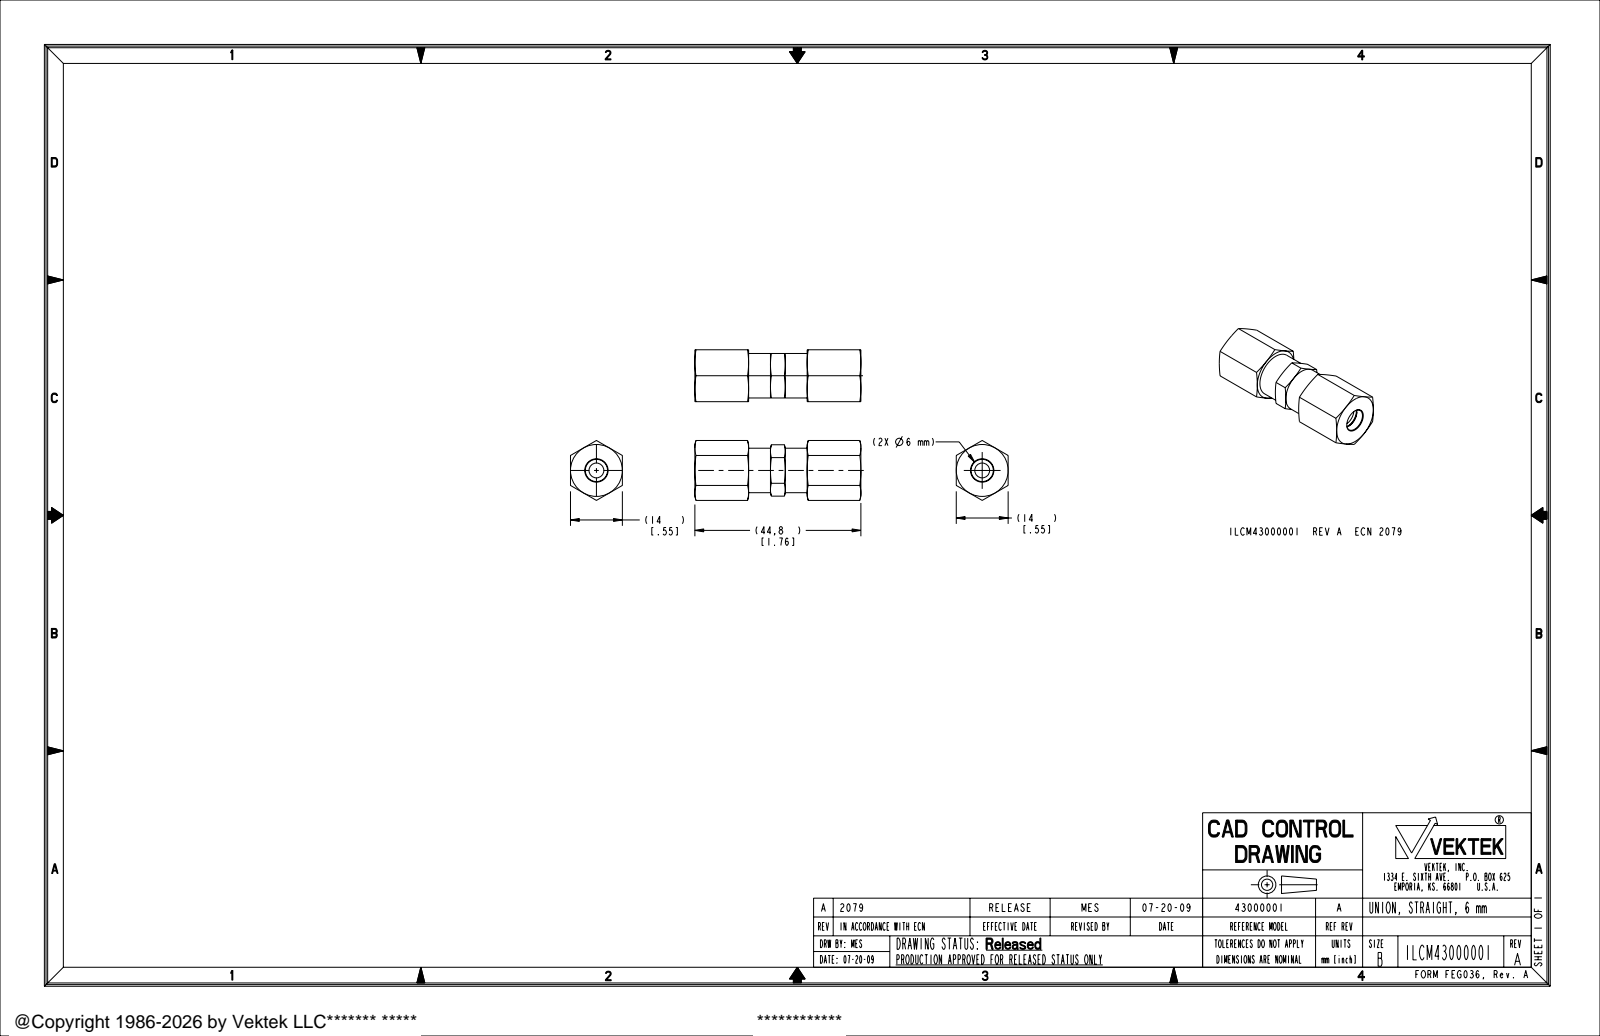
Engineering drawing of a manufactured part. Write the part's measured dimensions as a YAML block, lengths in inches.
part_name: "ILCM43000001"
step_written_by: "PRO/ENGINEER BY PARAMETRIC TECHNOLOGY CORPORATION, 2007460 (AUTOMOTIVE_DESIGN_CC2)"
units: inches
bodies: {solids: 1, faces: 130, planar: 32, cylindrical: 30, other: 68}
overall_size: [1.764, 0.636, 0.551]
volume: 0.325
surface_area: 6.459
round_holes:
  - {diameter: 0.157, count: 1}
  - {diameter: 0.236, count: 1}
  - {diameter: 0.409, count: 1}
round_bosses_or_shafts:
  - {diameter: 0.472, count: 1}
  - {diameter: 0.374, count: 1}
  - {diameter: 0.319, count: 1}
face_to_face_distances: [0.551, 0.039, 0.512, 1.764, 0.571, 1.193, 0.472, 0.409, 1.354, 0.161]
